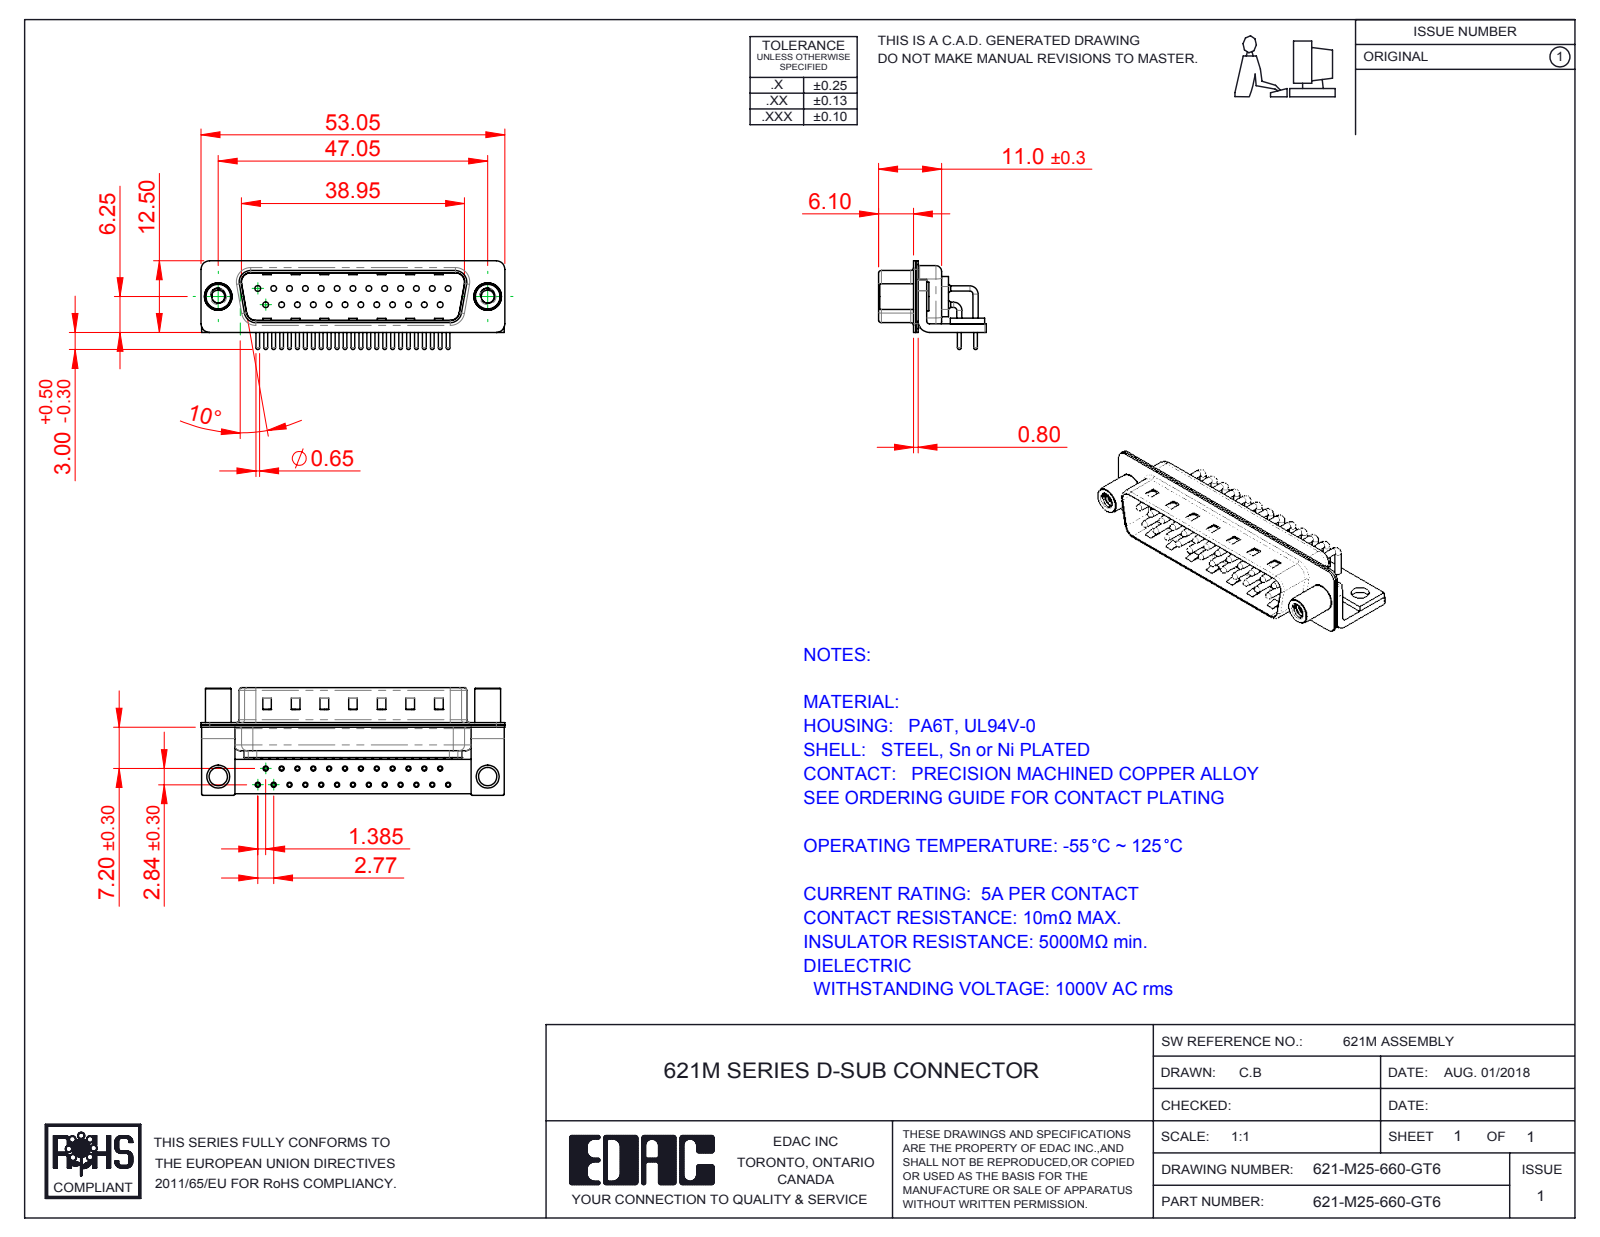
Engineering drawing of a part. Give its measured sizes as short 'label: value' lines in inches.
name: 621M Stabilizer Board_25 Contacts; 621M Housing_25 Contacts; 621M 4-40 Threaded Standoff; 621M Shell Rear_25 Contacts (+5 more)
written by: SolidWorks 2016 (CONFIG_CONTROL_DESIGN)
unit: in
bodies: 33 solids, 3276 faces (1799 planar, 1151 cylindrical, 326 other)
size: 2.089 × 0.74 × 0.61
volume: 0.214 in³; area: 14.27 in²
holes: 25× ⌀0.035, 25× ⌀0.039, 25× ⌀0.067, 25× ⌀0.079, 2× ⌀0.089, 2× ⌀0.126, 2× ⌀0.157, 2× ⌀0.189
bosses: 33× ⌀0.035, 25× ⌀0.059, 25× ⌀0.026, 2× ⌀0.197, 2× ⌀0.193, 2× ⌀0.177
rounds: 25× R0.04, 16× R0.01, 16× R0.059, 13× R0.079, 9× R0.02, 8× R0.063, 4× R0.024, 4× R0.026
face distances: 0.016, 0.033, 0.049, 0.059, 0.376, 0.031, 0.409, 0.327, 0.039, 0.075
hole spacings: 0.124, 0.109, 0.327, 0.218, 0.436, 0.545, 0.198, 0.654
